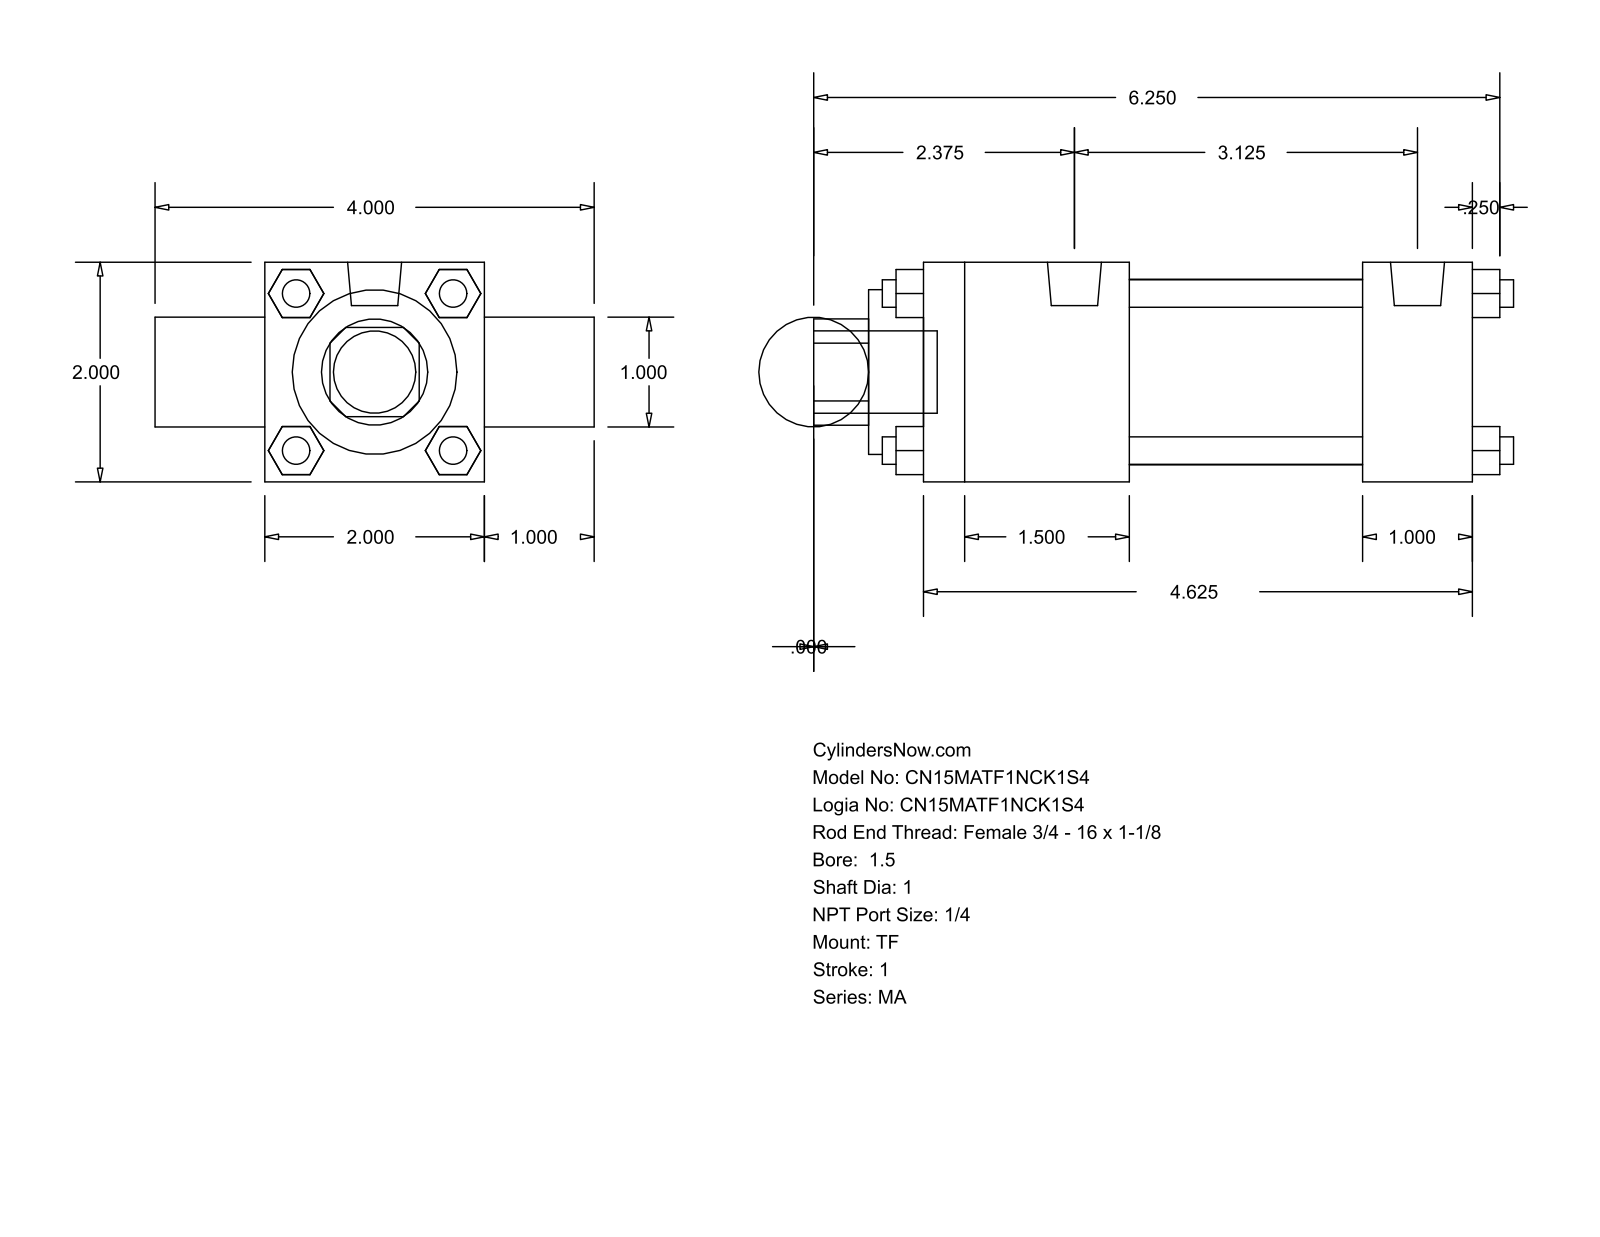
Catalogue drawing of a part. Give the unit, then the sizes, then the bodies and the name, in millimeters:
Units: millimetres
Overall size (bounding box): 161.93 × 101.6 × 50.8
Round holes (diameter × count): ⌀25.4 ×2, ⌀38.1 ×1, ⌀42.93 ×1
Round bosses / shafts (diameter × count): ⌀6.35 ×4, ⌀7.94 ×3, ⌀12.49 ×2, ⌀19.05 ×1
Partial cylindrical surfaces — rounded edges, fillets, slot ends (radius × count): R12.29 ×1
Main face-to-face distances: 50.8, 25.4, 101.6, 127, 76.2, 6.35, 47.63, 53.97, 79.37, 139.7
Bodies: 0 solids, 120 faces (92 planar, 28 cylindrical, 0 other)
Part name (STEP PRODUCT): MA_TF__0150_1
STEP written by: GSSL Pune (CONFIG_CONTROL_DESIGN)
